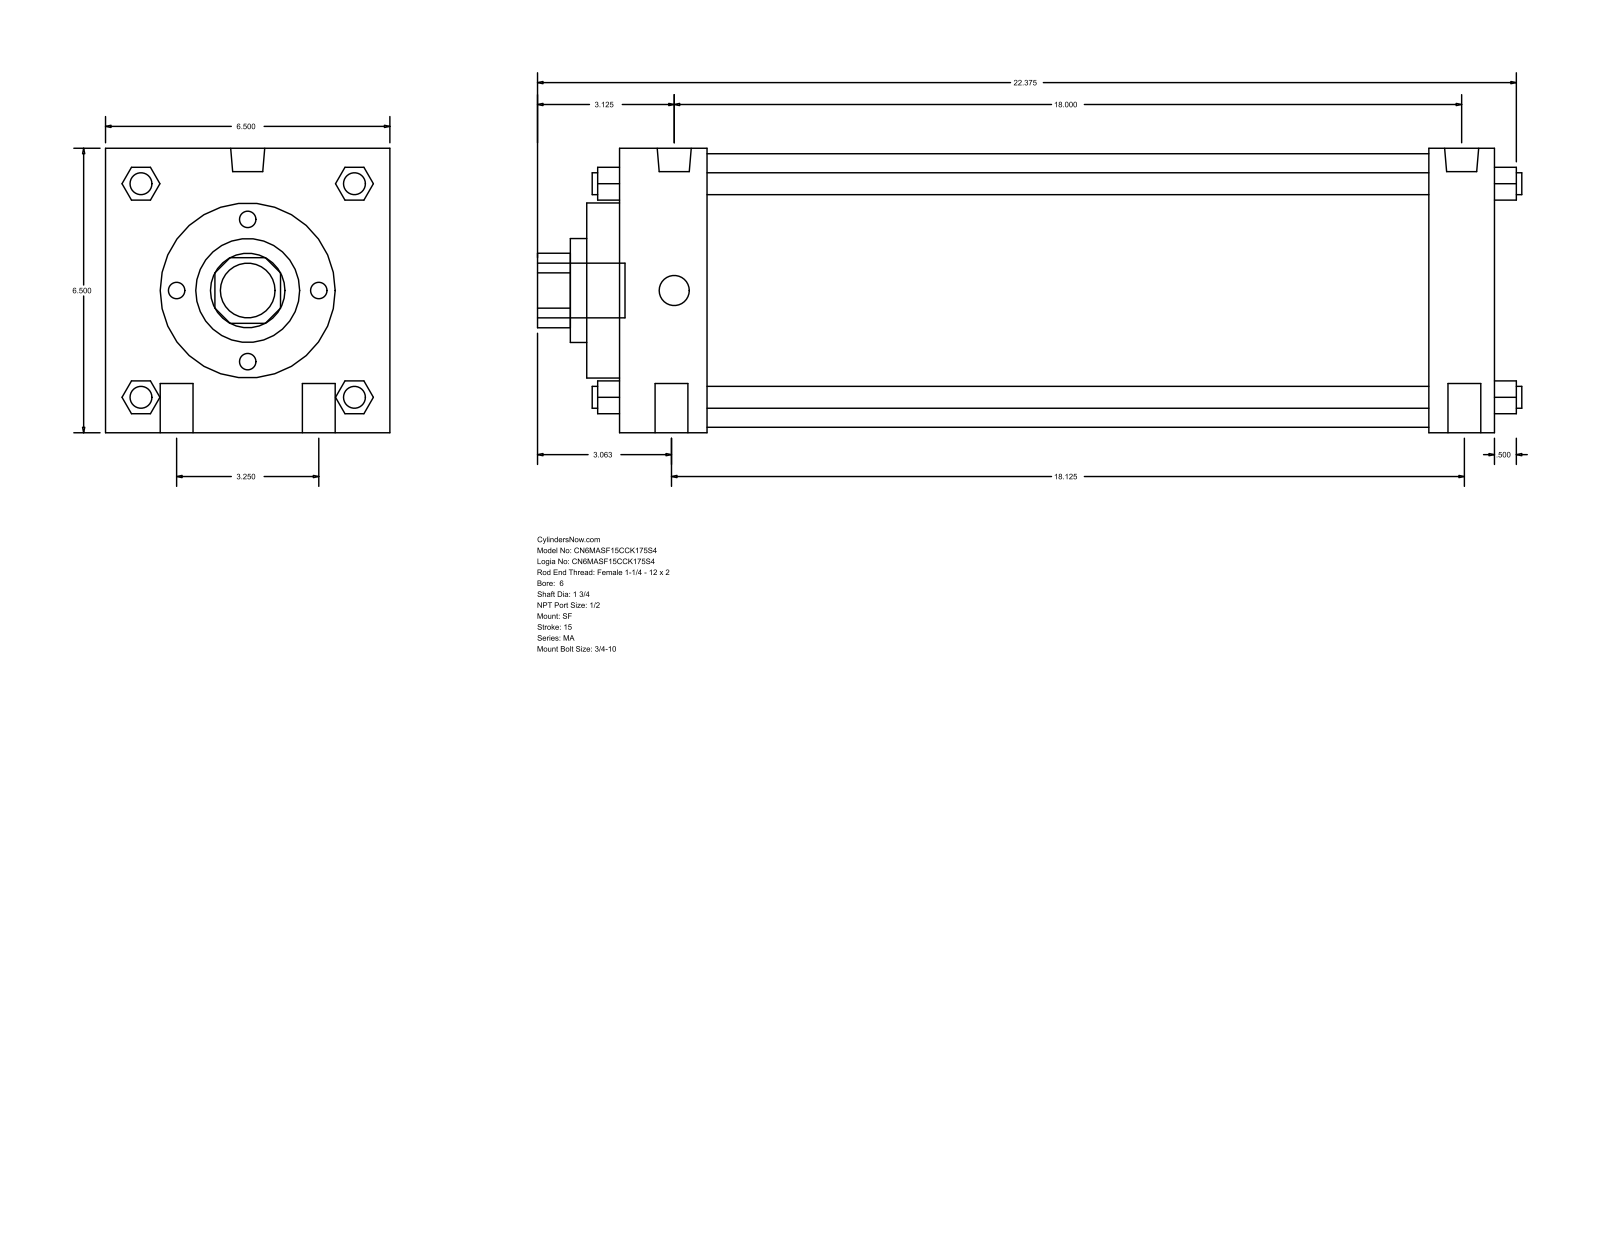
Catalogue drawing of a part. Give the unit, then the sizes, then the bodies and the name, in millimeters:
Units: millimetres
Overall size (bounding box): 571.5 × 165.1 × 165.1
Round holes (diameter × count): ⌀44.45 ×1, ⌀60.33 ×1, ⌀101.6 ×1, ⌀158.75 ×1
Round bosses / shafts (diameter × count): ⌀19.05 ×4, ⌀12.7 ×4, ⌀19.77 ×2, ⌀17.46 ×2, ⌀31.75 ×1
Partial cylindrical surfaces — rounded edges, fillets, slot ends (radius × count): R21.63 ×1
Main face-to-face distances: 165.1, 508, 19.05, 50.8, 38.1, 469.9, 419.1, 457.2, 69.85, 488.95
Bodies: 0 solids, 126 faces (95 planar, 31 cylindrical, 0 other)
Part name (STEP PRODUCT): MA_SF__0600_1.75
STEP written by: GSSL Pune (CONFIG_CONTROL_DESIGN)
